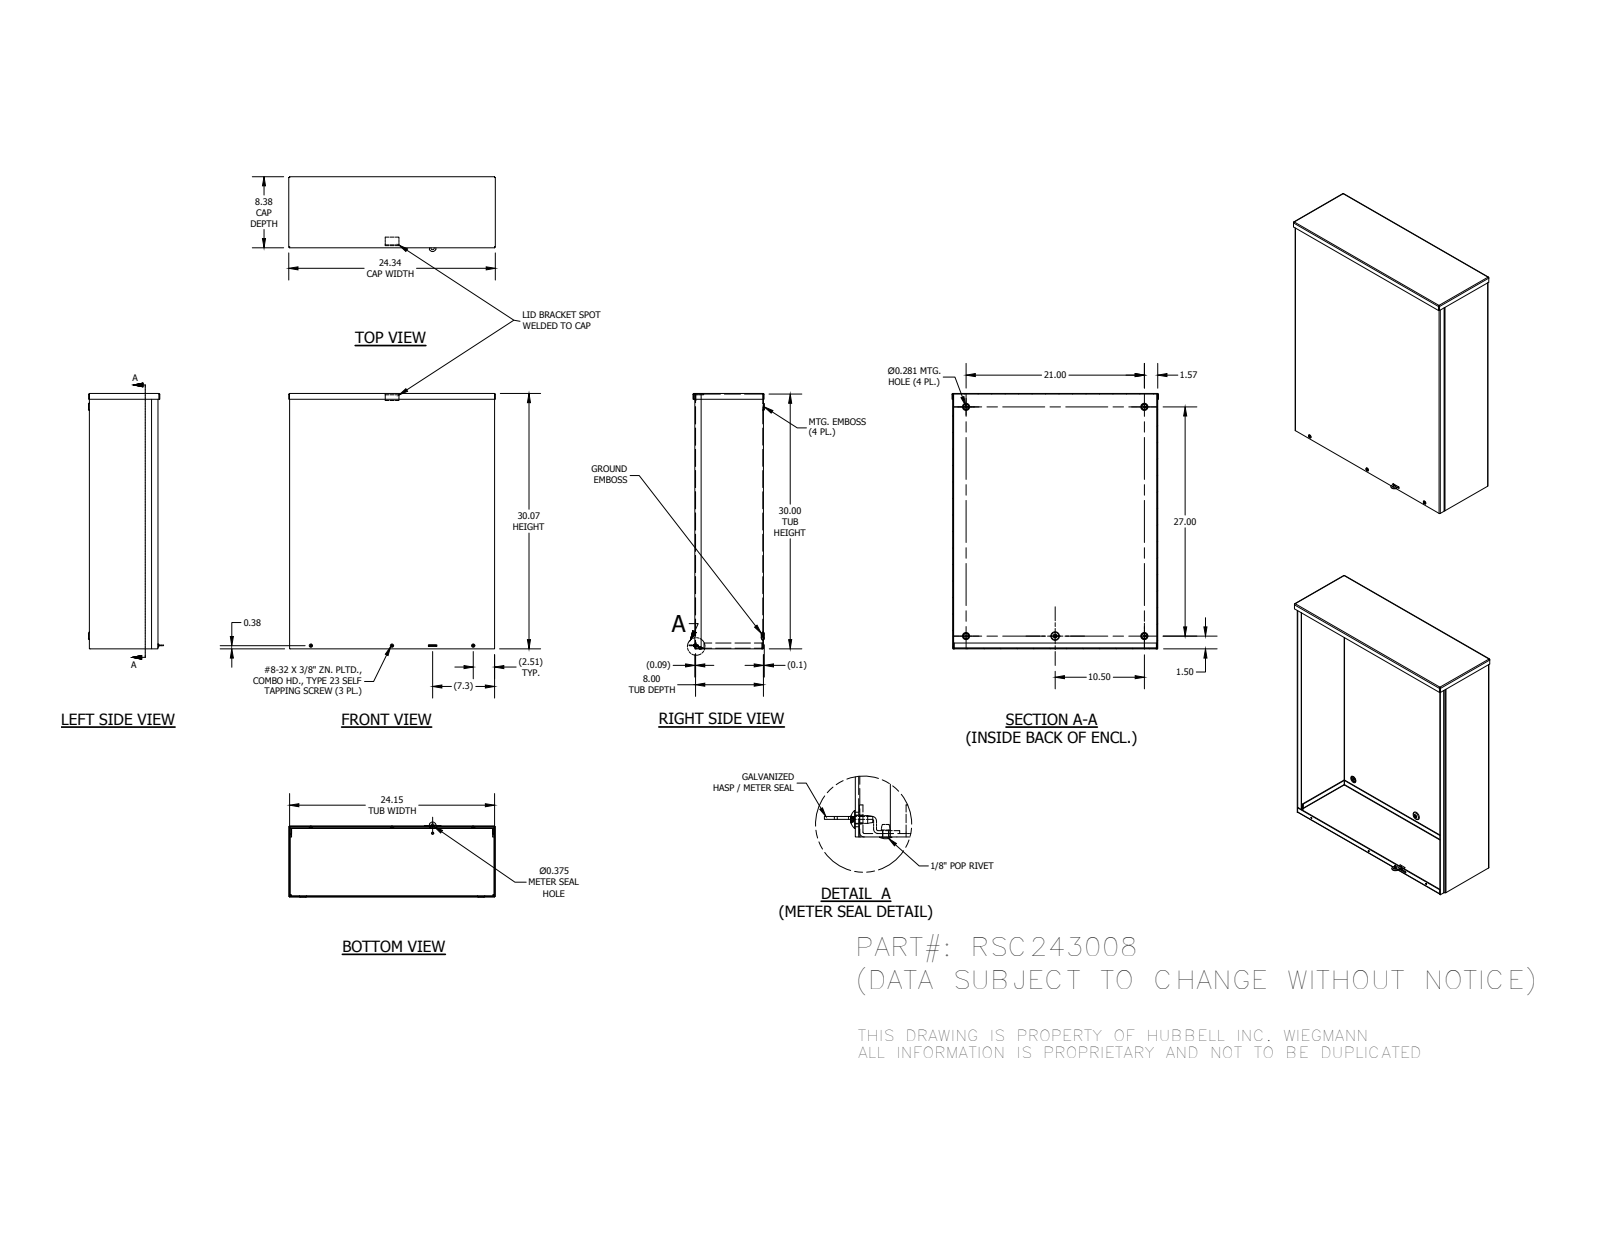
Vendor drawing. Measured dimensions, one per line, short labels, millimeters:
name: RSC243008BKPA; RSC2408EWPA; RSC2430LFA; RSC2408CPA (+5 more)
written by: Autodesk Inventor 2014 (AUTOMOTIVE_DESIGN)
unit: mm
bodies: 10 solids, 350 faces (193 planar, 66 cylindrical, 91 other)
size: 764.9 × 618.12 × 224.8
volume: 2 953 000 mm³; area: 3 163 000 mm²
holes: 6× ⌀7.94, 4× ⌀7.14, 3× ⌀3.73, 1× ⌀3.17, 1× ⌀3.45, 1× ⌀4.34, 1× ⌀9.52
bosses: 3× ⌀9.75, 3× ⌀4.17, 1× ⌀6.65, 1× ⌀5.93, 1× ⌀3.17
rounds: 19× R0.79, 17× R2.67, 2× R2.37, 1× R10.16
face distances: 1.88, 203.6, 205.48, 201.72, 611.48, 762, 609.6, 613.36, 763.88, 760.12
hole spacings: 242.89, 268.23, 510.39, 762.54, 781.65, 37.2, 485.78, 714.78
